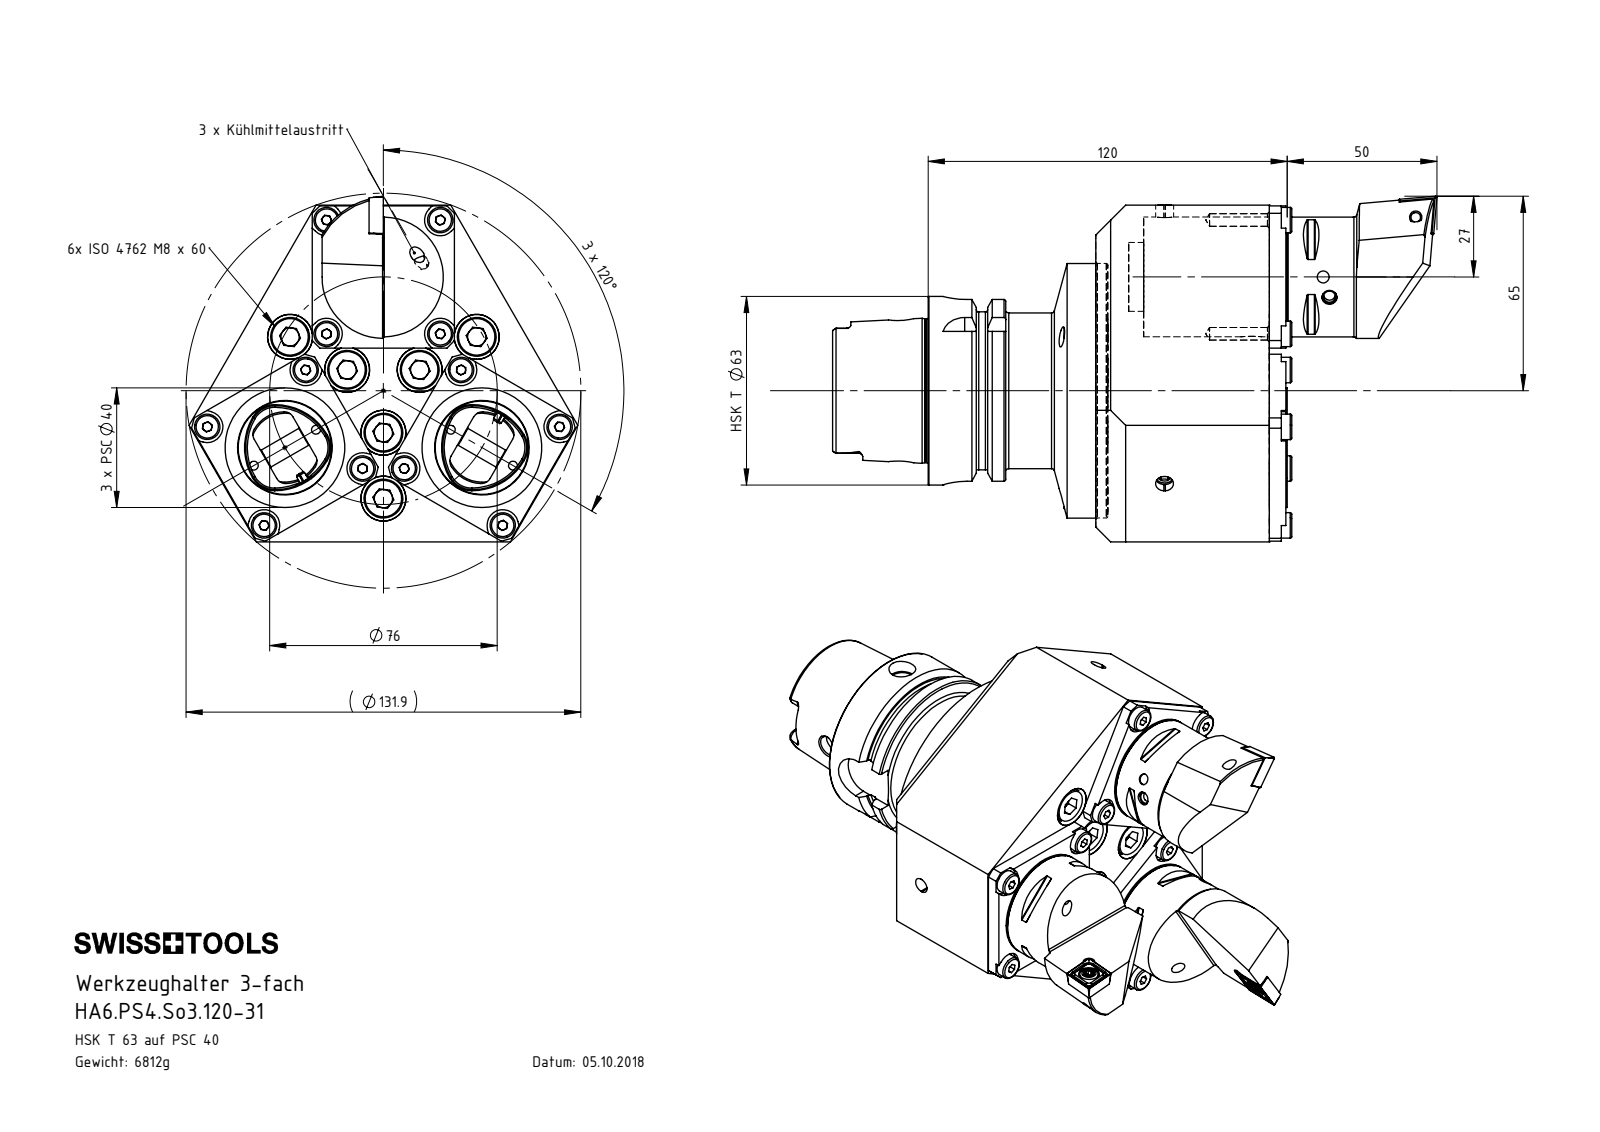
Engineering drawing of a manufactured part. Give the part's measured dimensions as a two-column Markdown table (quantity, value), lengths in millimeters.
| quantity | value |
| --- | --- |
| part name | U40-PS4.ER1.025_B; DIN 3771 - 37x1.5; DIN 6325_ø8x16_2x6; HA6-PS4.So3.060-31_A (+8 more) |
| STEP written by | SolidWorks 2017 (CONFIG_CONTROL_DESIGN) |
| units | millimeters |
| bodies | 55 solids, 2148 faces (833 planar, 542 cylindrical, 773 other) |
| overall size | 153.4 × 129.89 × 112.49 |
| volume | 733 557 mm³ |
| surface area | 196 219 mm² |
| round holes (diameter × count) | 4.2 × 12, 5.5 × 12, 2.5 × 9, 8.5 × 7, 3 × 6, 3.3 × 6, 6.8 × 6, 15 × 6, 2.1 × 3, 4 × 3, 5 × 3, 6 × 3 |
| round bosses / shafts (diameter × count) | 8.5 × 12, 5 × 12, 8 × 9, 3 × 9, 13 × 6, 5.5 × 6, 40 × 3, 39.7 × 3 |
| partial cylindrical surfaces (radius × count) | 3.5 × 12, 5.25 × 12, 1.4 × 6, 2.75 × 6, 3 × 6, 9 × 5, 2.88 × 4, 8 × 4 |
| main face-to-face distances | 54, 112.49, 12, 42, 47.5, 4, 2, 58, 16, 22.5 |
| hole center spacings | 38, 26.87, 44.68, 26.86, 32.19, 33.29, 33.35, 37.04 |
